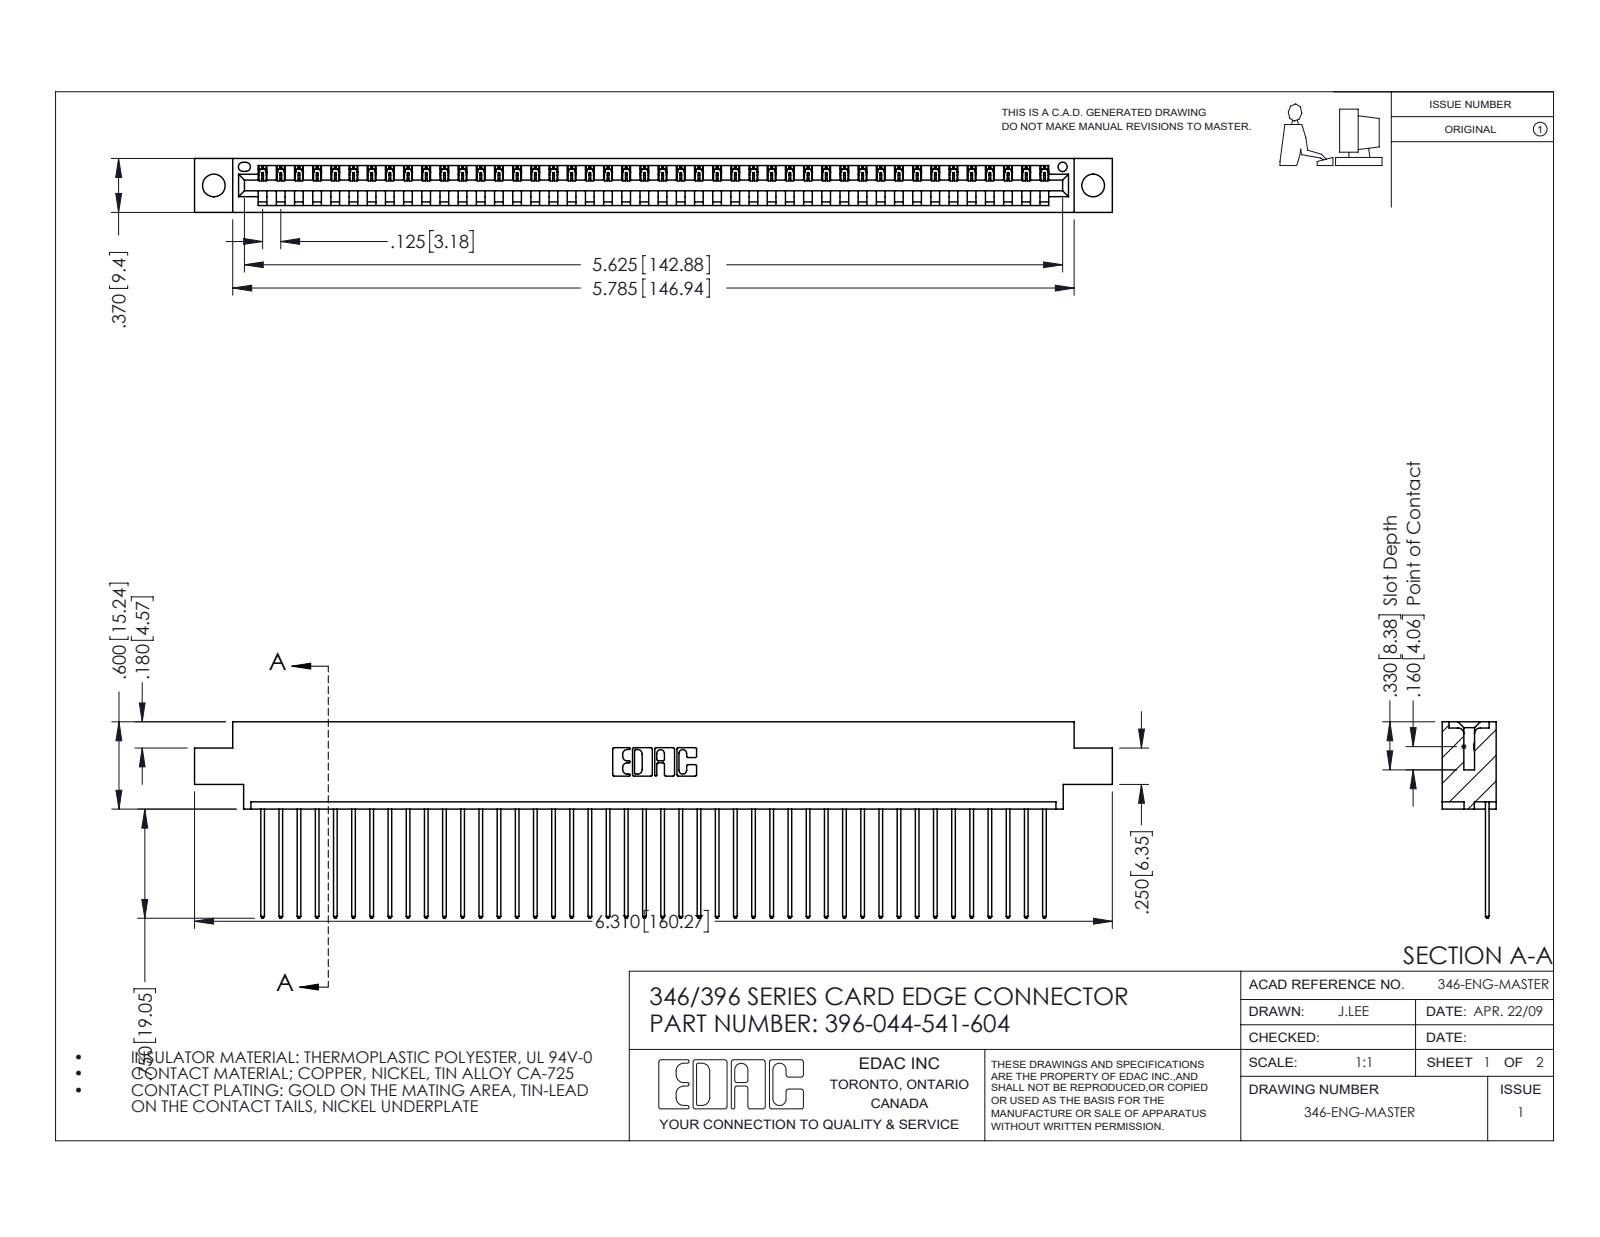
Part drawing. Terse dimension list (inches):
name: 345-292-001_345-293-141; 346 Part_0.170 Offset - 0.156 Dia-TH; 396-044-541-604
written by: SolidWorks 2016 (CONFIG_CONTROL_DESIGN)
unit: in
bodies: 45 solids, 2678 faces (1840 planar, 838 cylindrical, 0 other)
size: 6.31 × 1.35 × 0.37
volume: 0.931 in³; area: 30.88 in²
holes: 2× ⌀0.156, 1× ⌀0.064
rounds: 88× R0.006, 88× R0.01, 22× R0.01, 6× R0.007, 6× R0.031, 3× R0.026, 2× R0.031, 2× R0.04
face distances: 0.048, 0.322, 0.37, 0.25, 0.072, 0.298, 0.025, 0.148, 0.222, 0.1
hole spacings: 0.246, 5.836, 6.045
